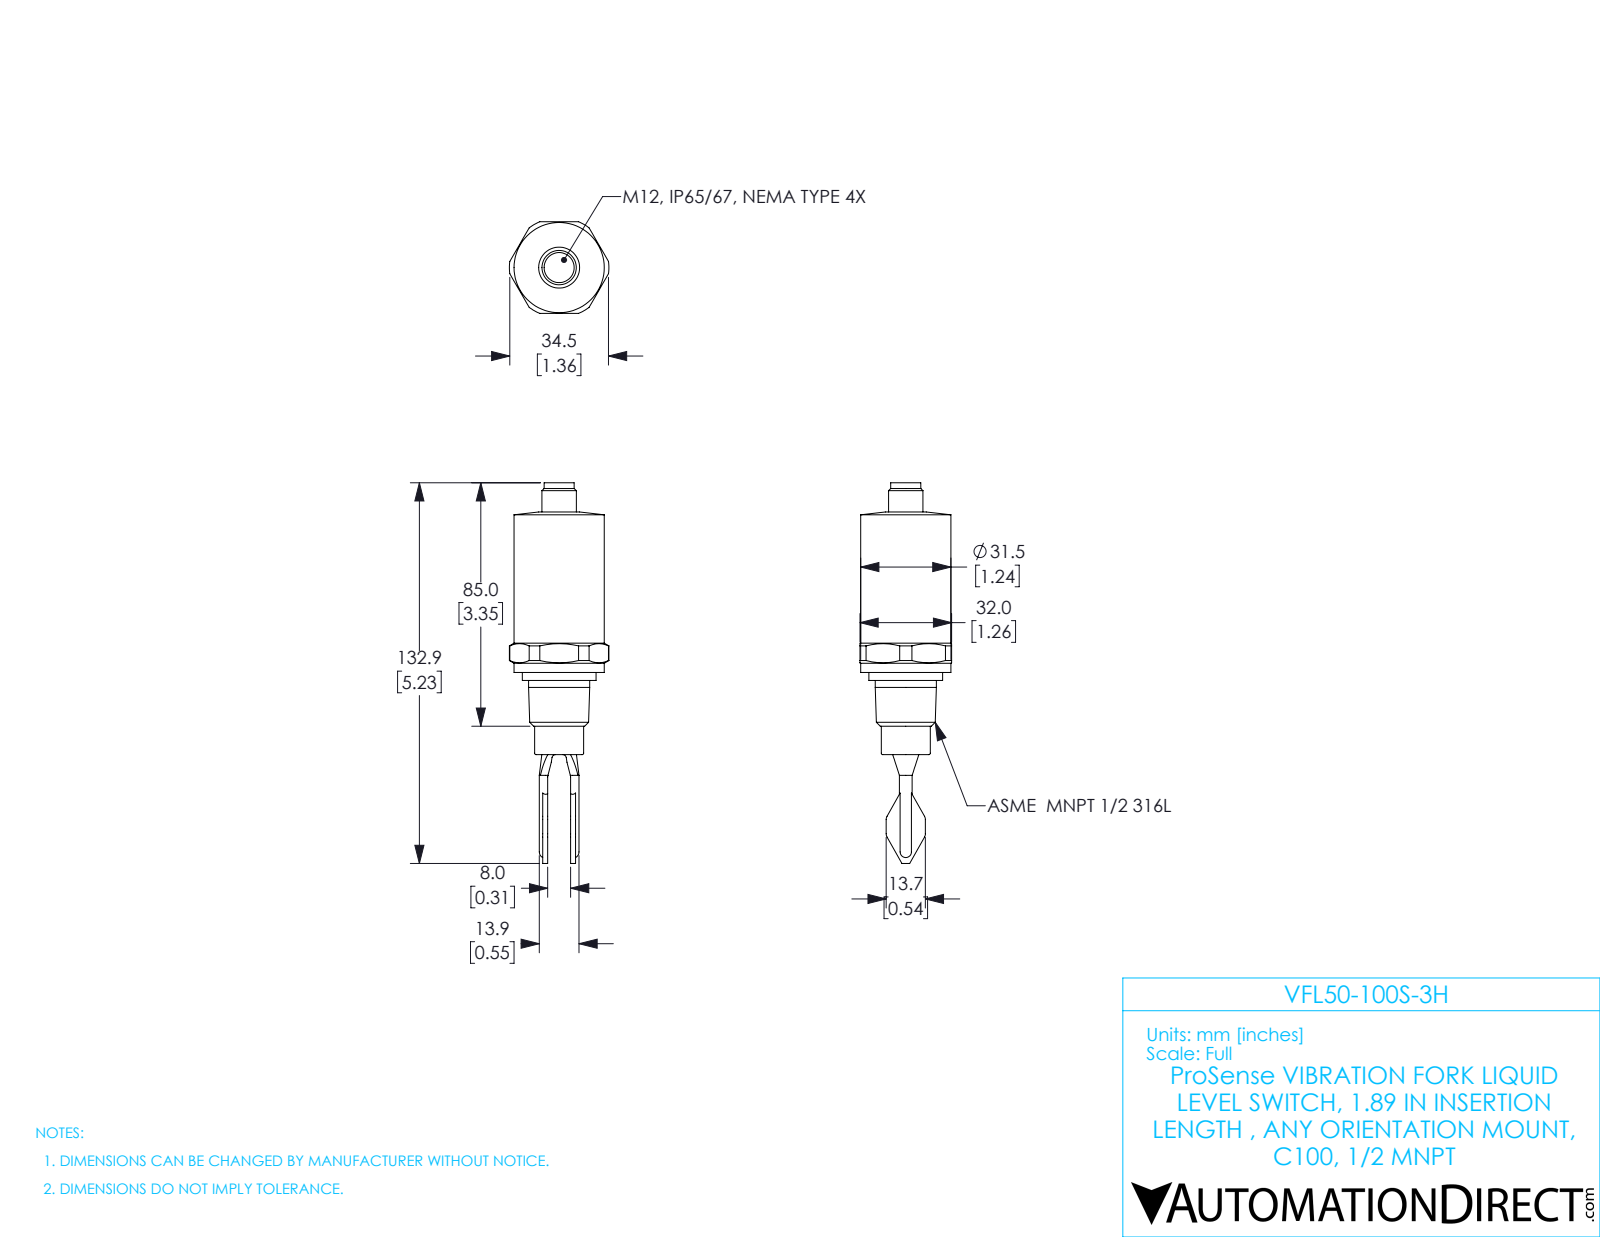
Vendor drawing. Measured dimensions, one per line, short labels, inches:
name: VFL50-100S-3H
written by: SolidWorks 2017 (AUTOMOTIVE_DESIGN)
unit: in
bodies: 1 solid, 101 faces (46 planar, 36 cylindrical, 19 other)
size: 5.232 × 1.368 × 1.26
volume: 3.393 in³; area: 16.77 in²
bosses: 1× ⌀1.24, 1× ⌀1.014, 1× ⌀0.84, 1× ⌀0.673, 1× ⌀0.472, 1× ⌀0.413
rounds: 4× R0.047, 4× R0.094, 2× R0.088, 1× R0.684
face distances: 0.068, 0.383, 0.315, 1.26, 0.11, 0.451, 1.02, 1.13, 3.736, 2.717
